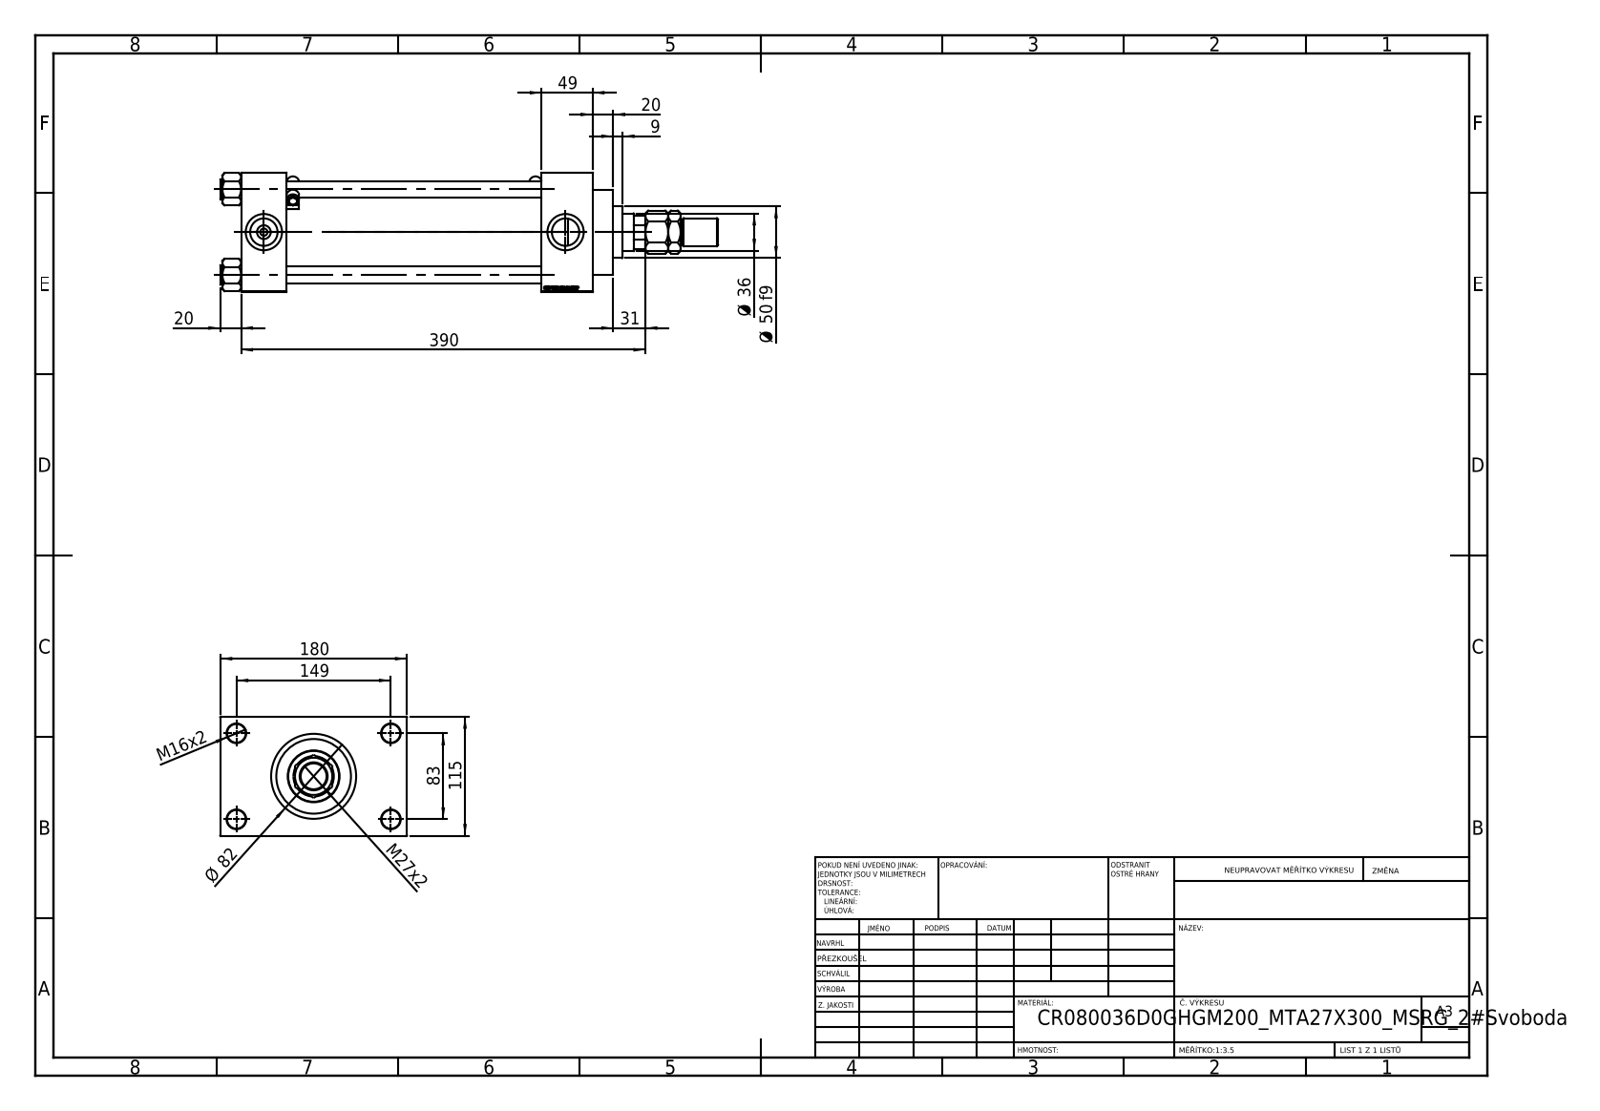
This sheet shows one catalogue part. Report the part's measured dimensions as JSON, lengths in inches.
{"part_name": "V215CR_VCP_D; V215CR_D_TYCINKA; V215_VC_A; NUT_M5_D (+3 more)", "step_written_by": "SolidWorks 2019 (CONFIG_CONTROL_DESIGN)", "units": "inches", "bodies": {"solids": 14, "faces": 1264, "planar": 596, "cylindrical": 120, "other": 548}, "overall_size": [18.898, 7.087, 4.528], "volume_in3": 153.4, "surface_area_in2": 714.8, "round_holes": [[0.63, 4], [0.709, 4], [0.276, 2], [1.041, 2], [1.378, 2], [1.004, 1], [1.417, 1], [1.535, 1], [2.402, 1], [2.835, 1], [3.15, 1]], "round_bosses_or_shafts": [[0.748, 4], [0.197, 2], [0.098, 2], [3.386, 1], [3.228, 1], [1.969, 1], [1.063, 1], [0.984, 1]], "partial_cylinders_radius": [[0.02, 12], [0.236, 4], [0.689, 1]], "face_to_face_distances": [4.528, 9.685, 11.614, 1.929, 1.732, 11.417, 13.346, 1.28, 5.807, 7.087], "hole_center_spacings": [1.305, 2.302, 3.256, 3.357, 3.513, 4.561, 5.607, 3.268]}
